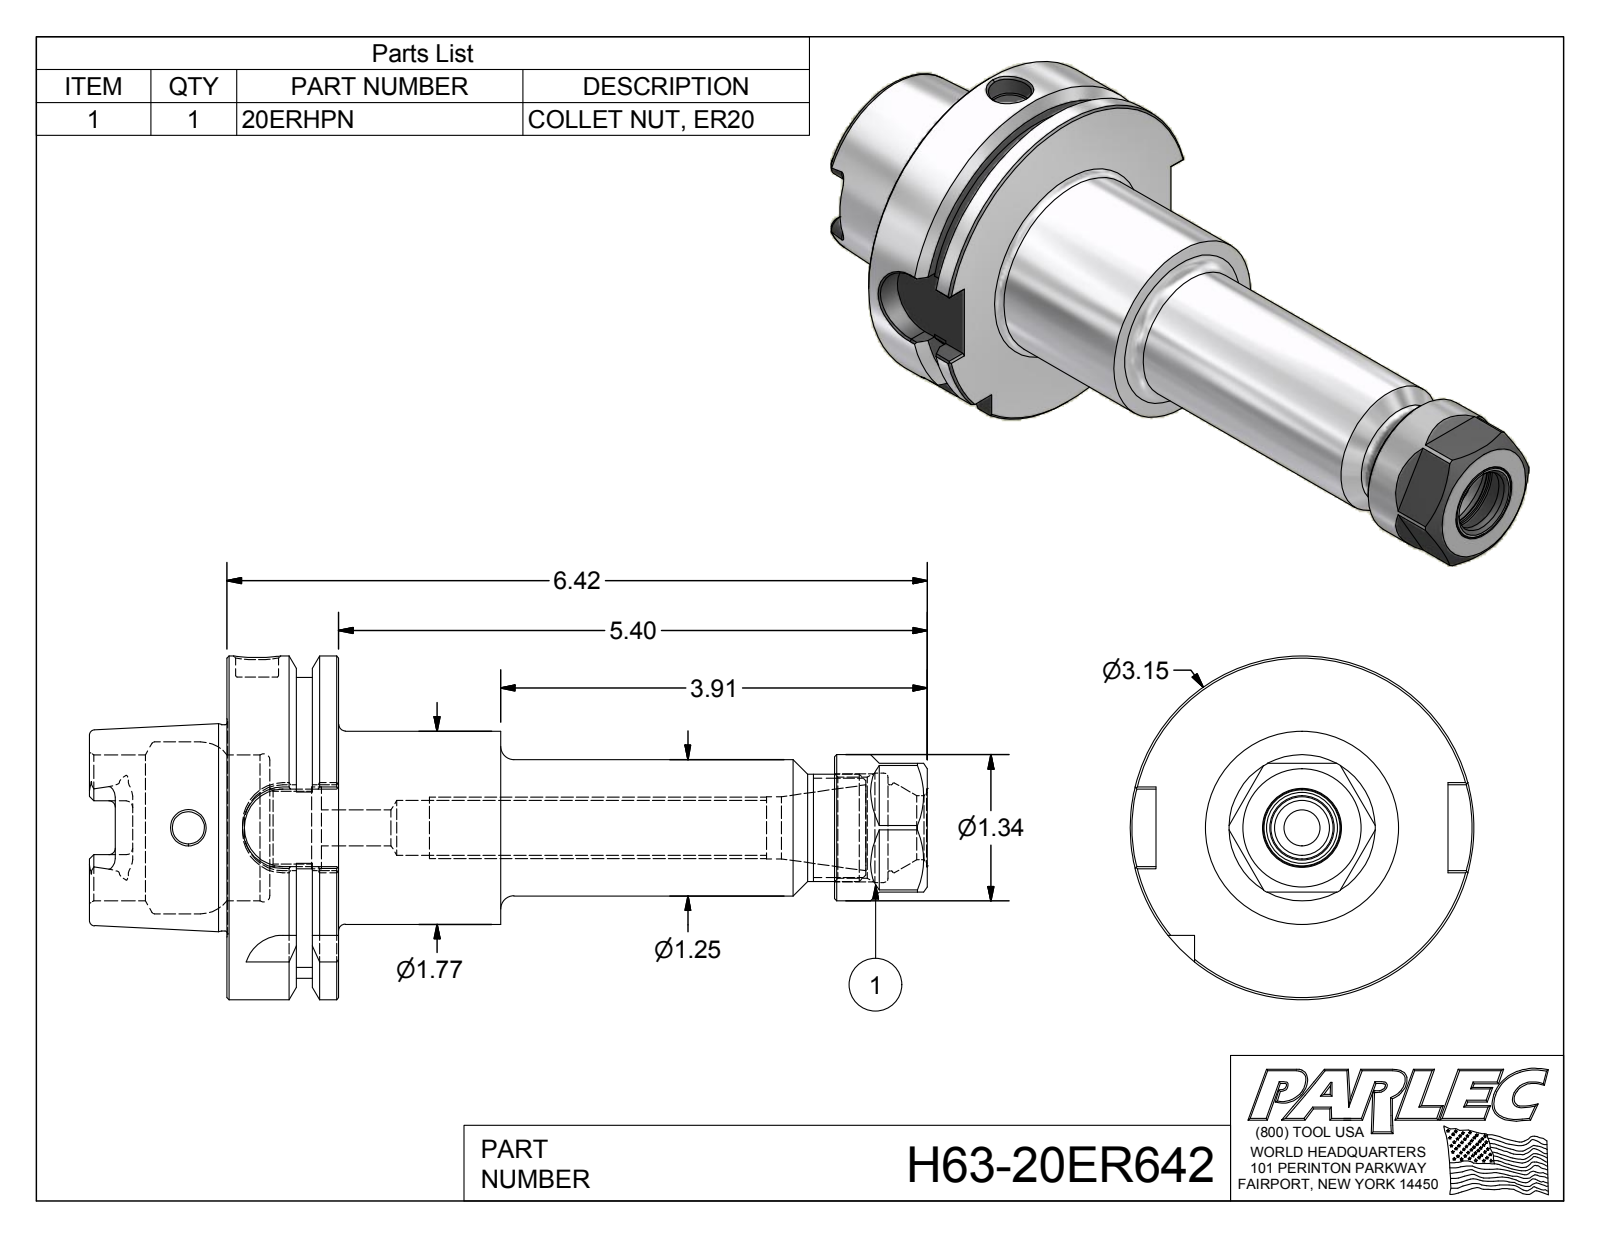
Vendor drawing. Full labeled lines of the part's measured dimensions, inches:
Part name (STEP PRODUCT): H63-20ER642; H63-20ER6-1; BS-09; 20ERHPN
STEP written by: Autodesk Inventor 2012 (AUTOMOTIVE_DESIGN)
Units: inches
Bodies: 3 solids, 201 faces (86 planar, 46 cylindrical, 69 other)
Overall size (bounding box): 7.68 × 3.15 × 3.15
Volume: 14.94 in³ · Surface area: 80.56 in²
Round holes (diameter × count): ⌀0.281 ×1, ⌀0.295 ×1, ⌀0.33 ×1, ⌀0.331 ×1, ⌀0.394 ×1, ⌀0.502 ×1, ⌀0.57 ×1, ⌀0.587 ×1, ⌀0.666 ×1, ⌀0.749 ×1, ⌀0.79 ×1, ⌀0.926 ×1
Round bosses / shafts (diameter × count): ⌀3.15 ×1, ⌀1.891 ×1, ⌀1.77 ×1, ⌀1.34 ×1, ⌀1.25 ×1, ⌀0.984 ×1, ⌀0.555 ×1, ⌀0.422 ×1
Partial cylindrical surfaces — rounded edges, fillets, slot ends (radius × count): R0.059 ×6, R0.113 ×4, R0.354 ×4, R1.378 ×1
Main face-to-face distances: 1.024, 0.241, 0.389, 0.394, 0.63, 0.783, 0.635, 0.148, 1.18, 2.509
